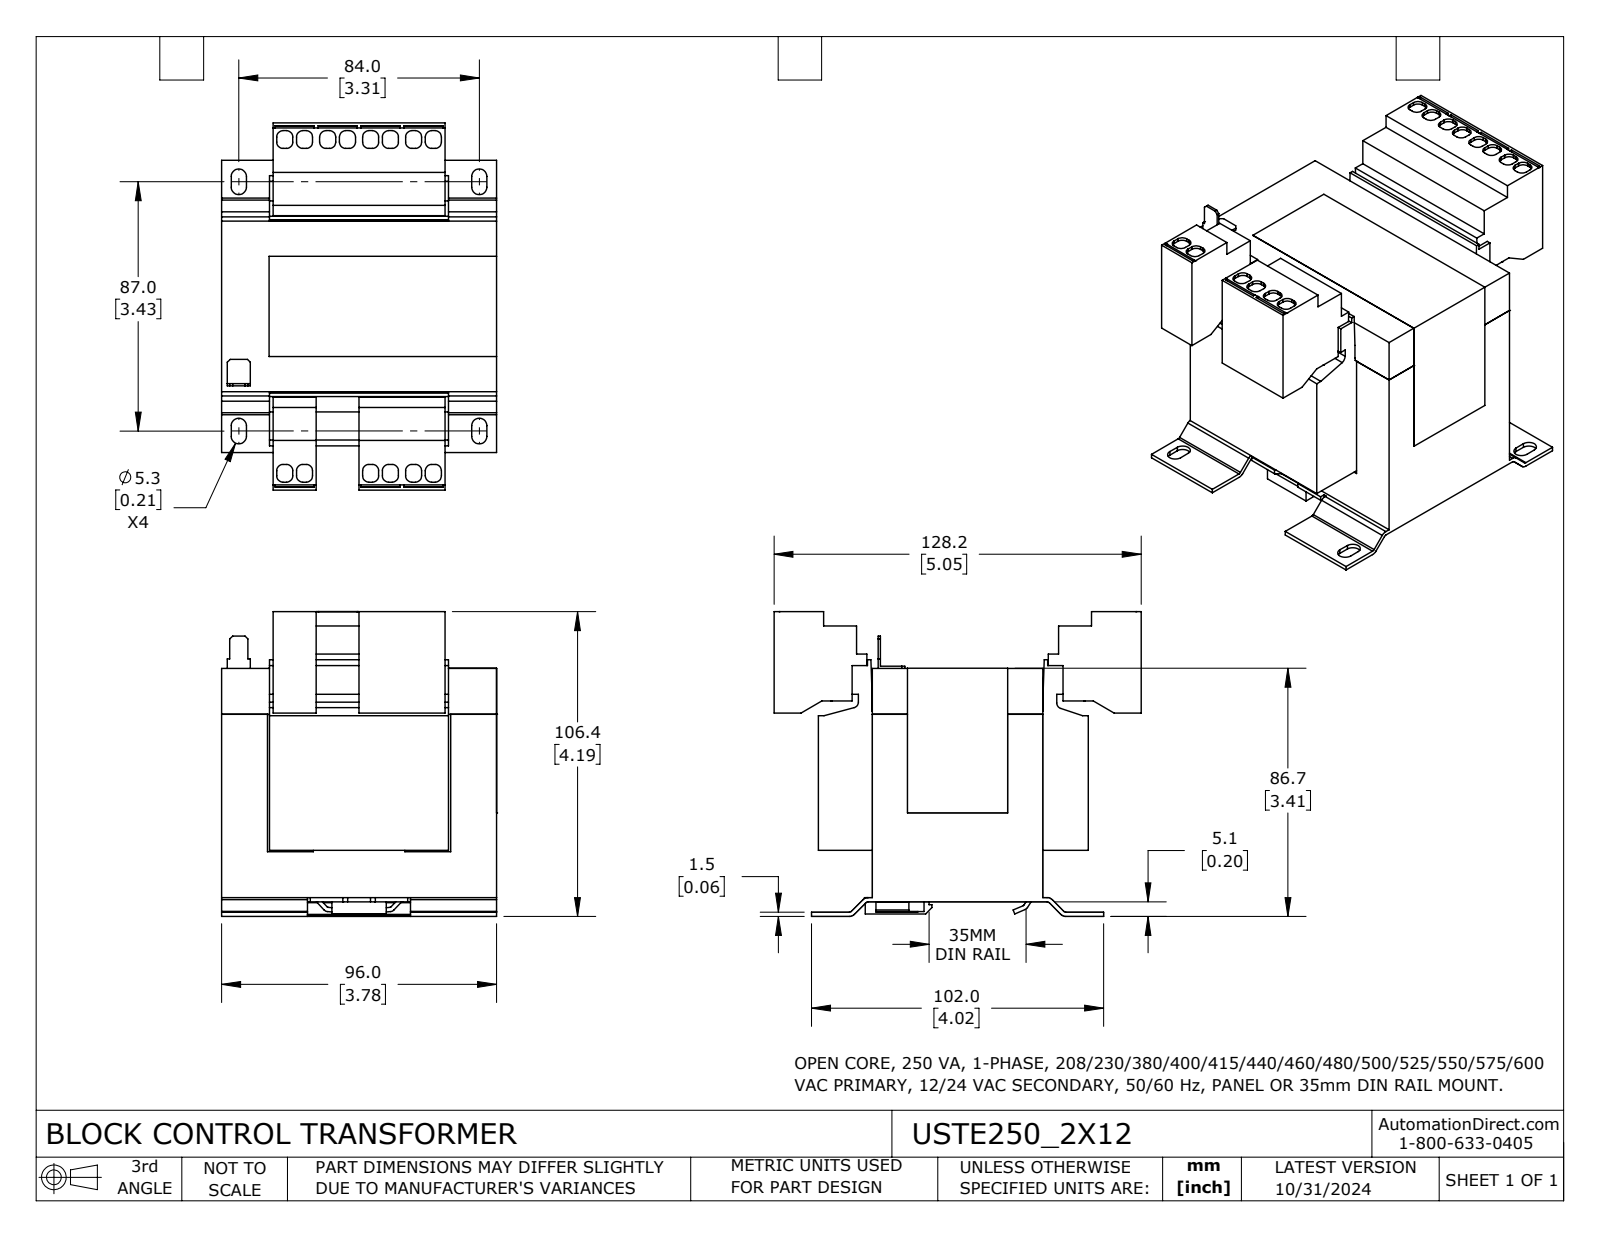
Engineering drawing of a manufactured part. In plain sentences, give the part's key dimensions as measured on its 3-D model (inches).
The part is named "USTE250_2X12". Its 3-D file was written by "SolidWorks 2023 (CONFIG_CONTROL_DESIGN)". It is 1 solid with 503 faces: 409 planar, 90 cylindrical and 4 other. Overall it measures 5.047 by 4.19 by 3.782 inches. Its volume is 40.38 cubic inches and its surface area 161.1 square inches. Partial cylindrical surfaces (rounded edges, fillets, slot ends): 56 of radius 0.087, 8 of radius 0.104, 5 of radius 0.079, 4 of radius 0.039, 4 of radius 0.098, 3 of radius 0.02. The main face-to-face distances are 0.63, 0.659, 3.12, 0.709, 3.15, 0.03, 2.49, 2.52, 2.461, 2.343.
